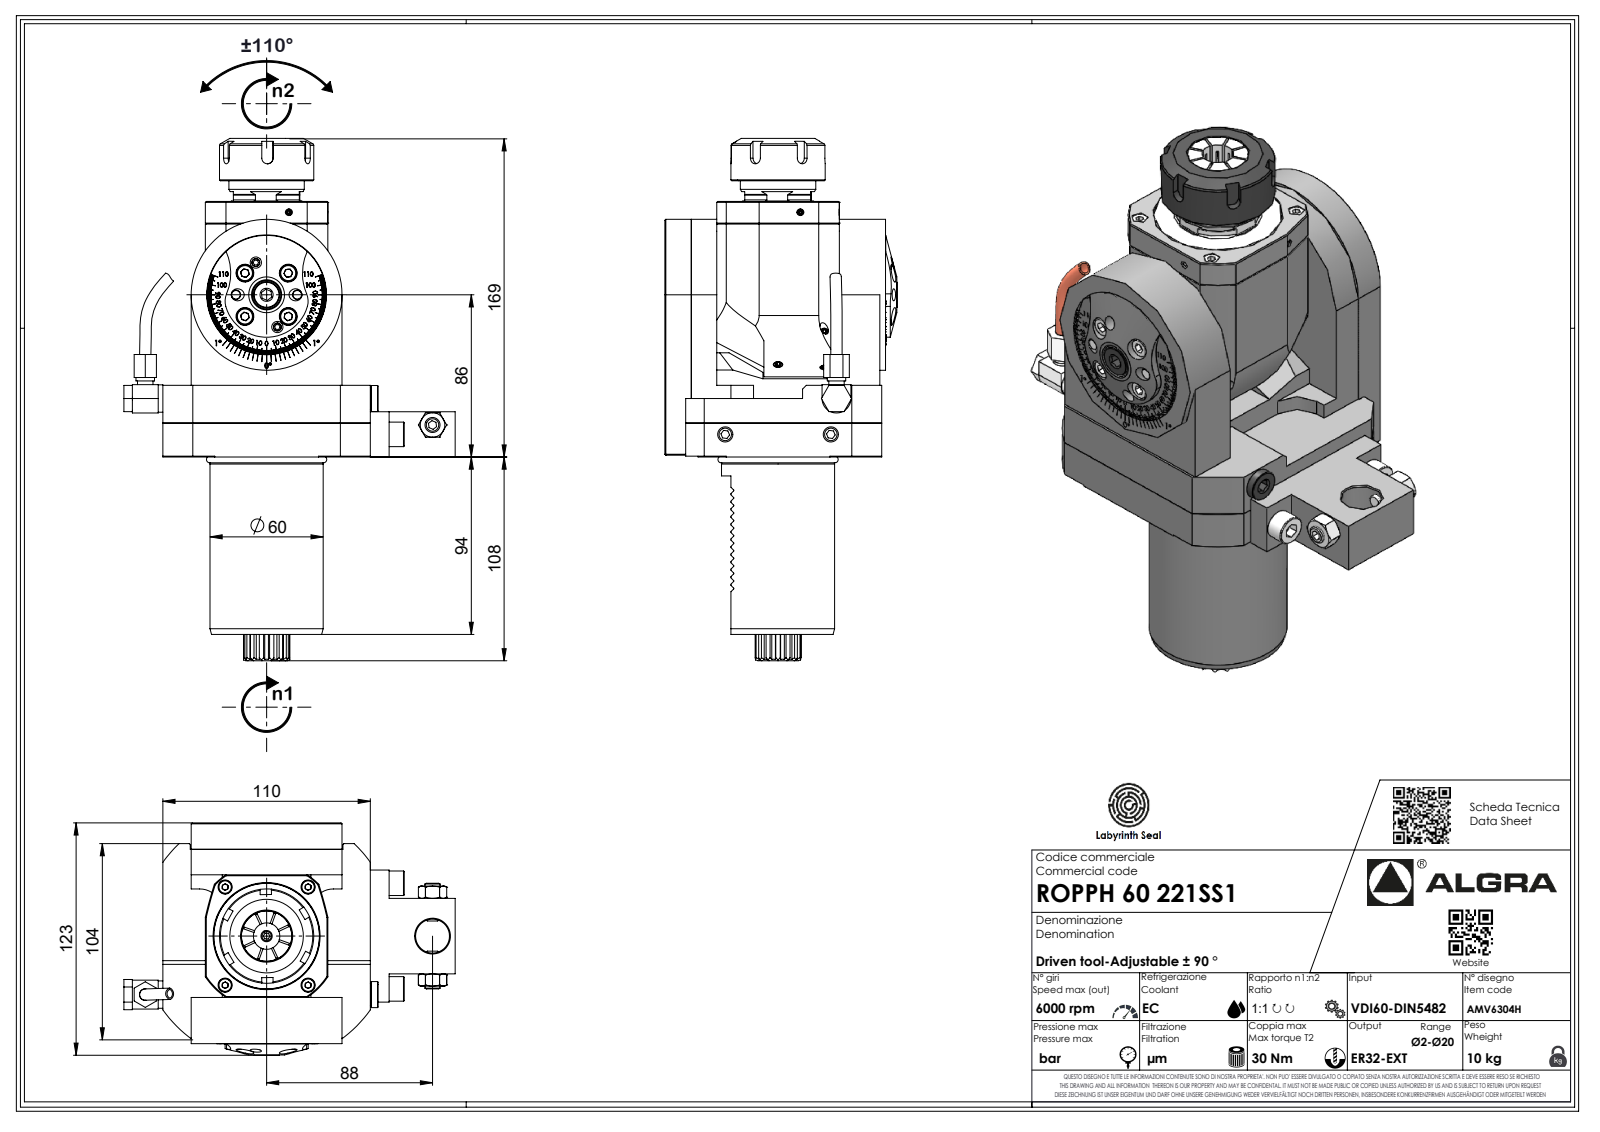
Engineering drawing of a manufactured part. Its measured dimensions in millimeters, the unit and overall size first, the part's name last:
Units: millimetres
Overall size (bounding box): 276.91 × 175.7 × 123
Round holes (diameter × count): ⌀2.1 ×1, ⌀44.2 ×1, ⌀48.2 ×1, ⌀52.2 ×1, ⌀56.2 ×1
Round bosses / shafts (diameter × count): ⌀80 ×1, ⌀60 ×1, ⌀58.7 ×1, ⌀56 ×1, ⌀52 ×1, ⌀50 ×1, ⌀44 ×1, ⌀40 ×1
Partial cylindrical surfaces — rounded edges, fillets, slot ends (radius × count): R0.3 ×14, R0.33 ×7, R0.52 ×7, R3.7 ×7, R3 ×5, R0.2 ×3, R10 ×2, R12 ×2
Main face-to-face distances: 22.5, 87.5, 65, 80, 7.5, 7, 95, 135.5, 27.5, 94
Volume: 1 485 000 mm³ · Surface area: 127 513 mm²
Bodies: 1 solid, 703 faces (430 planar, 132 cylindrical, 141 other)
Part name (STEP PRODUCT): ROPPH60221SS1
STEP written by: SolidWorks 2023 (AUTOMOTIVE_DESIGN)
